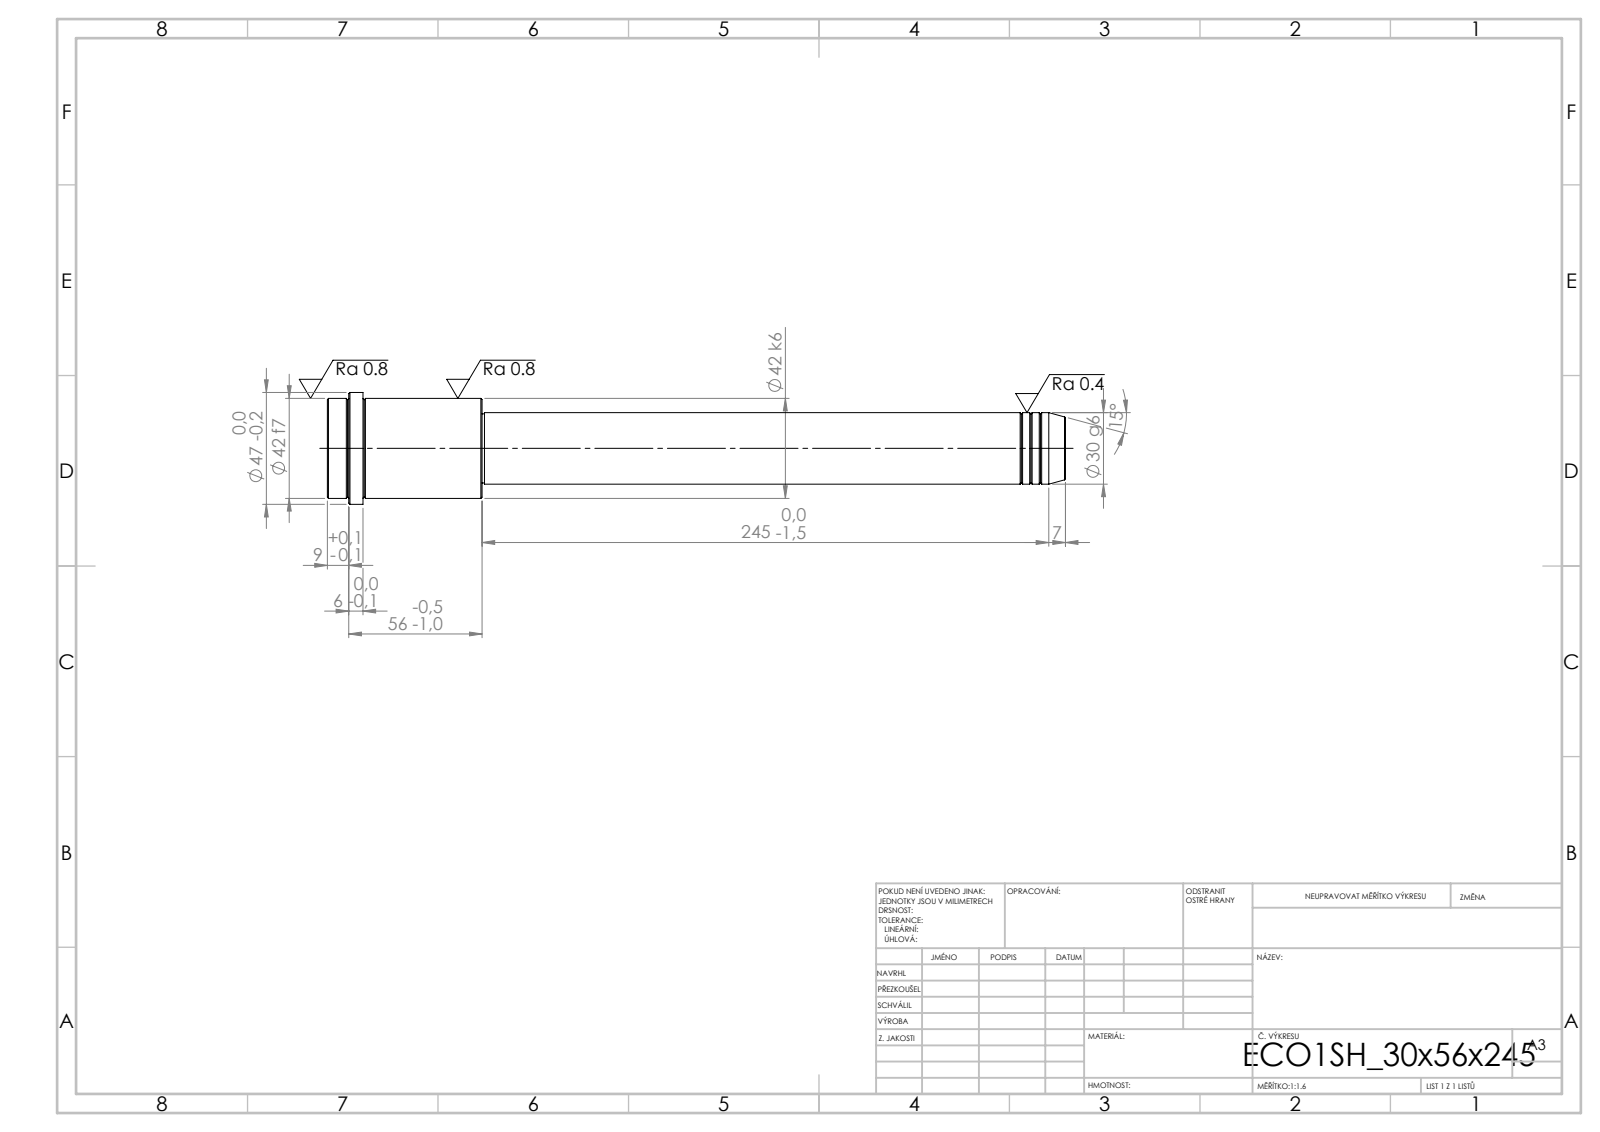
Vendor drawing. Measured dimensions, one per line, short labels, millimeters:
written by: SolidWorks 2019 (CONFIG_CONTROL_DESIGN)
unit: mm
bodies: 1 solid, 52 faces (6 planar, 16 cylindrical, 30 other)
size: 310 × 47 × 47
volume: 264 426 mm³; area: 35 301 mm²
bosses: 1× ⌀47, 1× ⌀42, 1× ⌀30, 1× ⌀29
face distances: 65, 245, 310, 295, 50, 15, 301, 56, 6, 9
